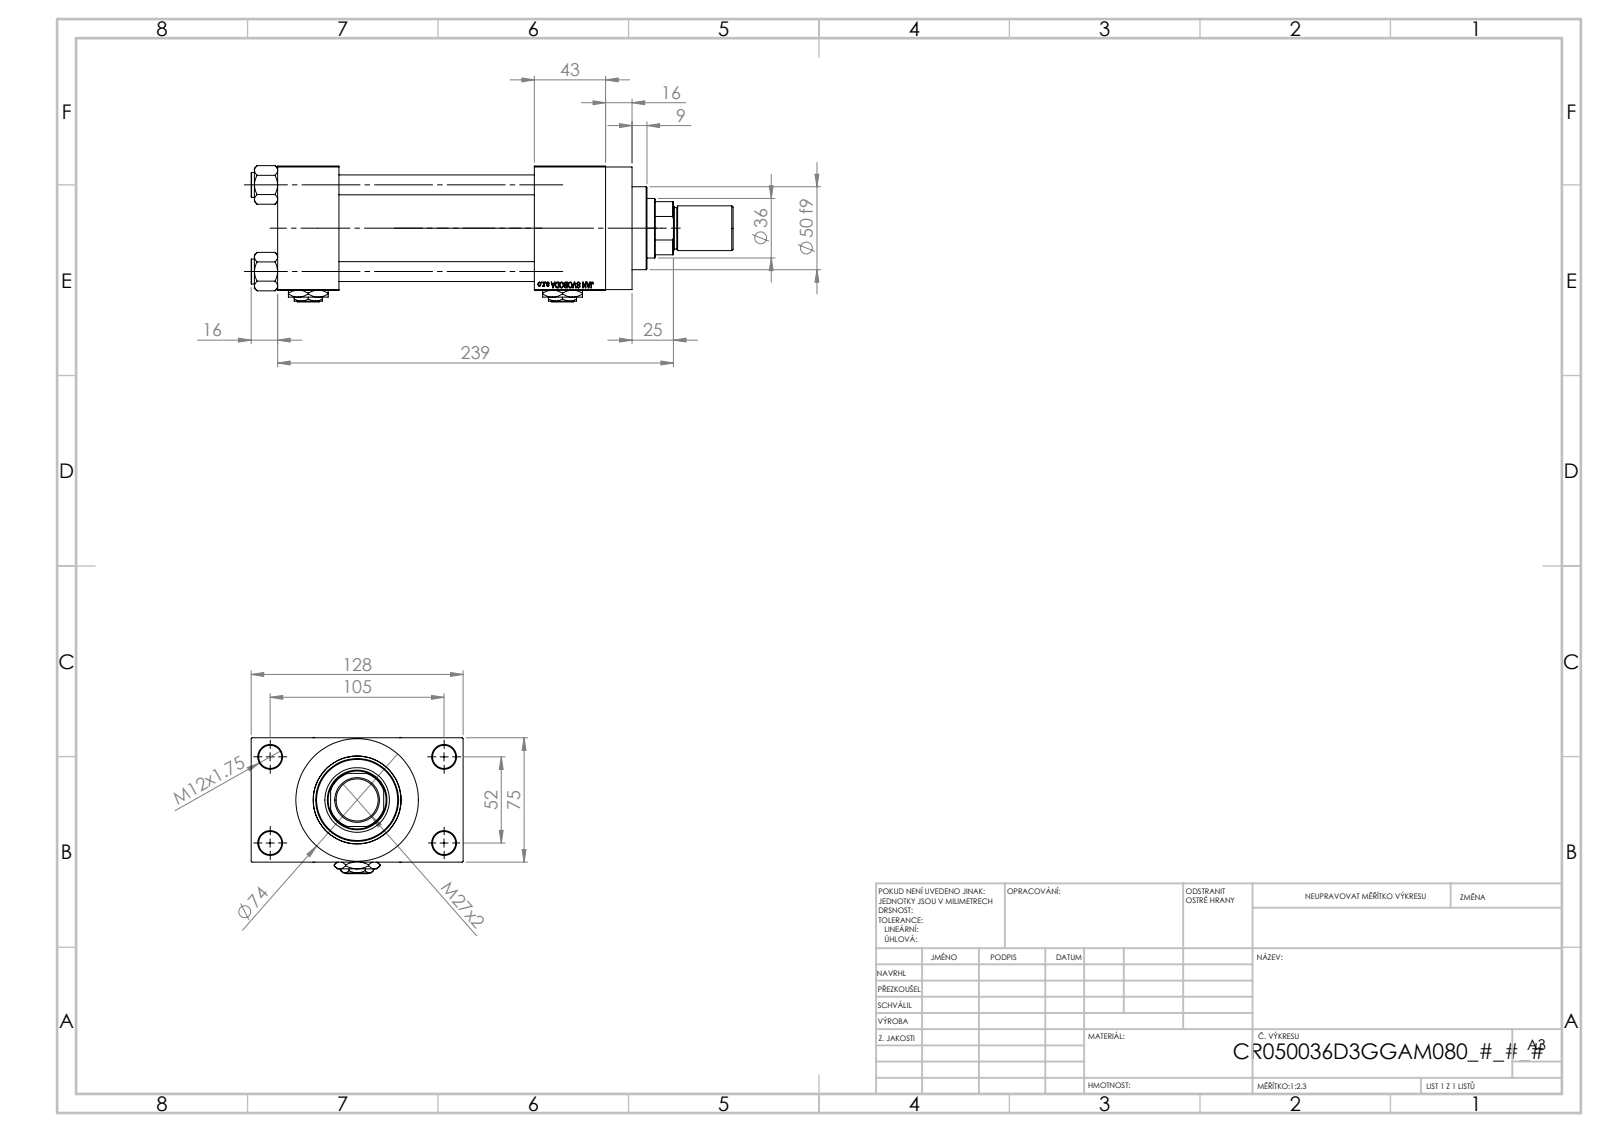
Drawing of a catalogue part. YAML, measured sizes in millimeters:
part_name: "V215CR_D_Body; V215CR_D_TYCINKA; V215CR_VCP_D; NUT_M5_D (+3 more)"
step_written_by: "SolidWorks 2019 (CONFIG_CONTROL_DESIGN)"
units: millimeters
bodies: {solids: 14, faces: 1219, planar: 549, cylindrical: 104, other: 566}
overall_size: [291, 128, 82.27]
volume: 960574
surface_area: 218109
round_holes:
  - {diameter: 12, count: 4}
  - {diameter: 14, count: 4}
  - {diameter: 7, count: 2}
  - {diameter: 20.96, count: 2}
  - {diameter: 30, count: 2}
  - {diameter: 25.5, count: 1}
  - {diameter: 36, count: 1}
  - {diameter: 39, count: 1}
  - {diameter: 41, count: 1}
  - {diameter: 53, count: 1}
round_bosses_or_shafts:
  - {diameter: 15, count: 4}
  - {diameter: 74, count: 1}
  - {diameter: 56, count: 1}
  - {diameter: 50, count: 1}
  - {diameter: 27, count: 1}
  - {diameter: 25, count: 1}
partial_cylinders:
  - {radius: 17.5, count: 1}
face_to_face_distances: [75, 118, 37, 155, 26.5, 101.5, 198, 43, 161, 16]
hole_center_spacings: [26.35, 36.98, 52.3, 58.43, 58.59, 78.65, 94.37, 52]
